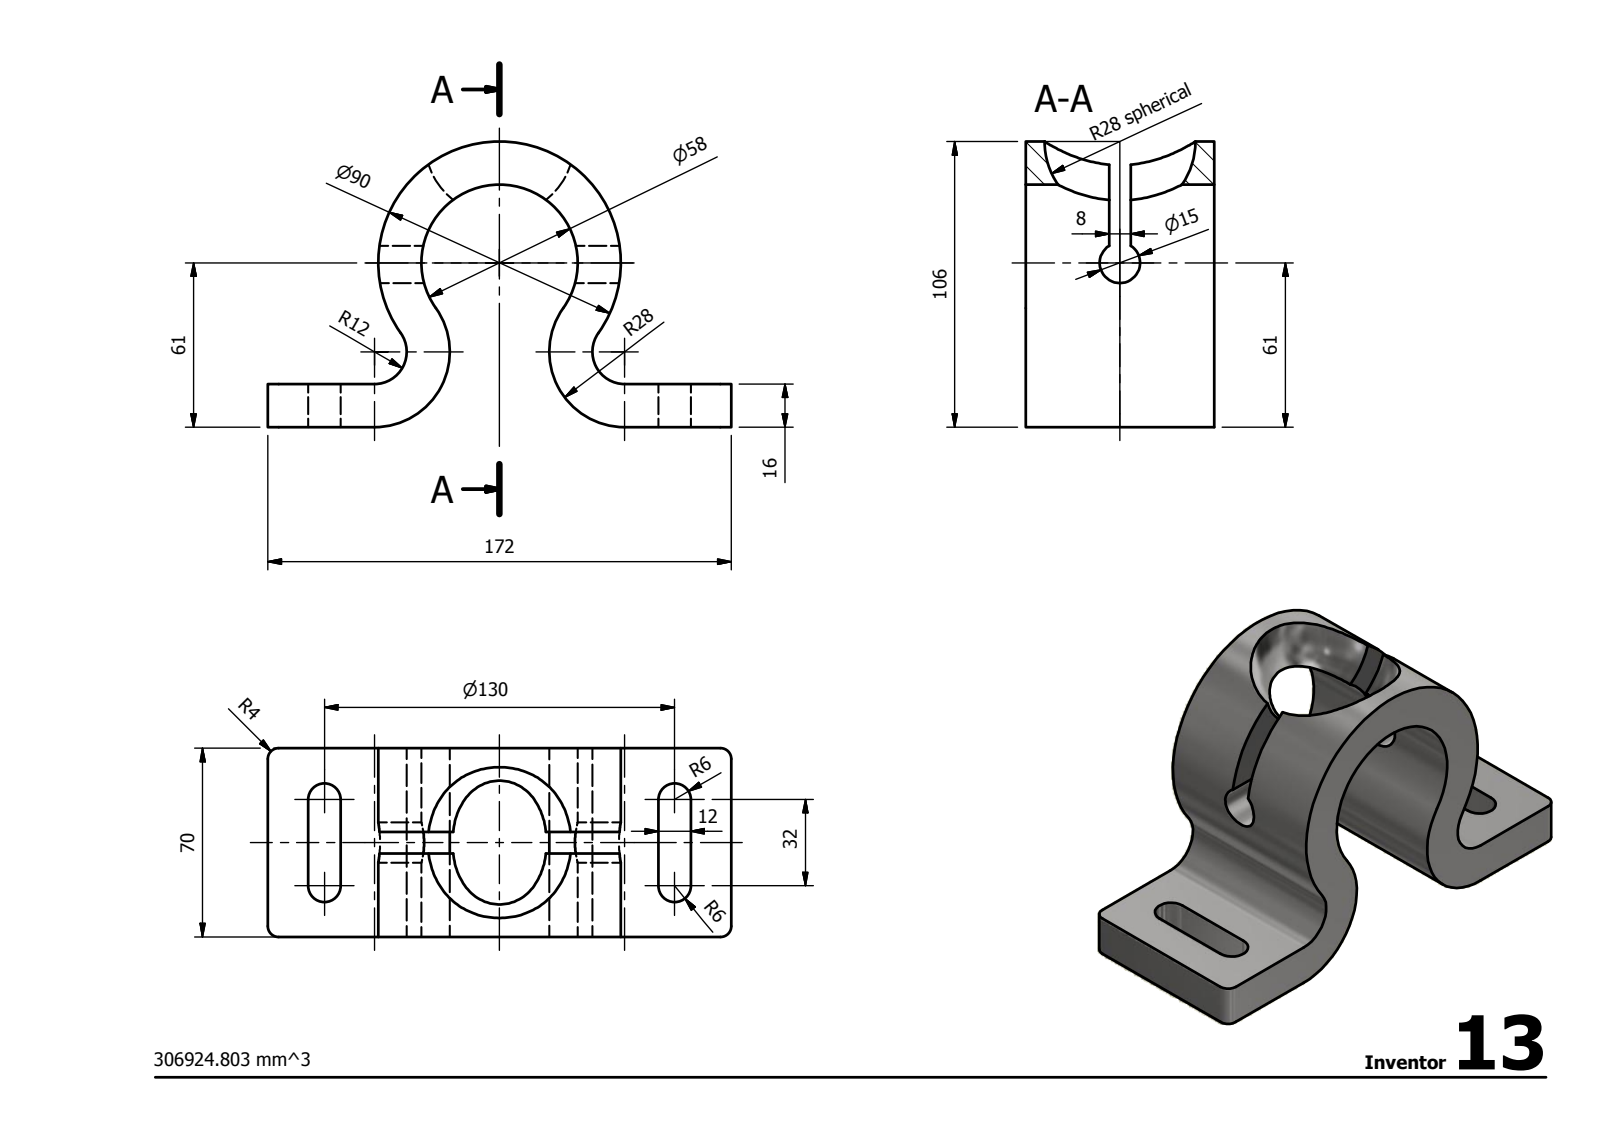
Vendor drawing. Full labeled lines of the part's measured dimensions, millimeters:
STEP written by: Autodesk Inventor 2014 (AUTOMOTIVE_DESIGN)
Units: millimetres
Bodies: 1 solid, 34 faces (16 planar, 16 cylindrical, 2 other)
Overall size (bounding box): 172 × 106 × 70
Volume: 306 855 mm³ · Surface area: 59 815 mm²
Round holes (diameter × count): ⌀15 ×1
Partial cylindrical surfaces — rounded edges, fillets, slot ends (radius × count): R4 ×4, R6 ×4, R12 ×2, R28 ×2, R29 ×1, R45 ×1
Main face-to-face distances: 70, 16, 31, 39, 15, 27, 145, 157, 12, 130
